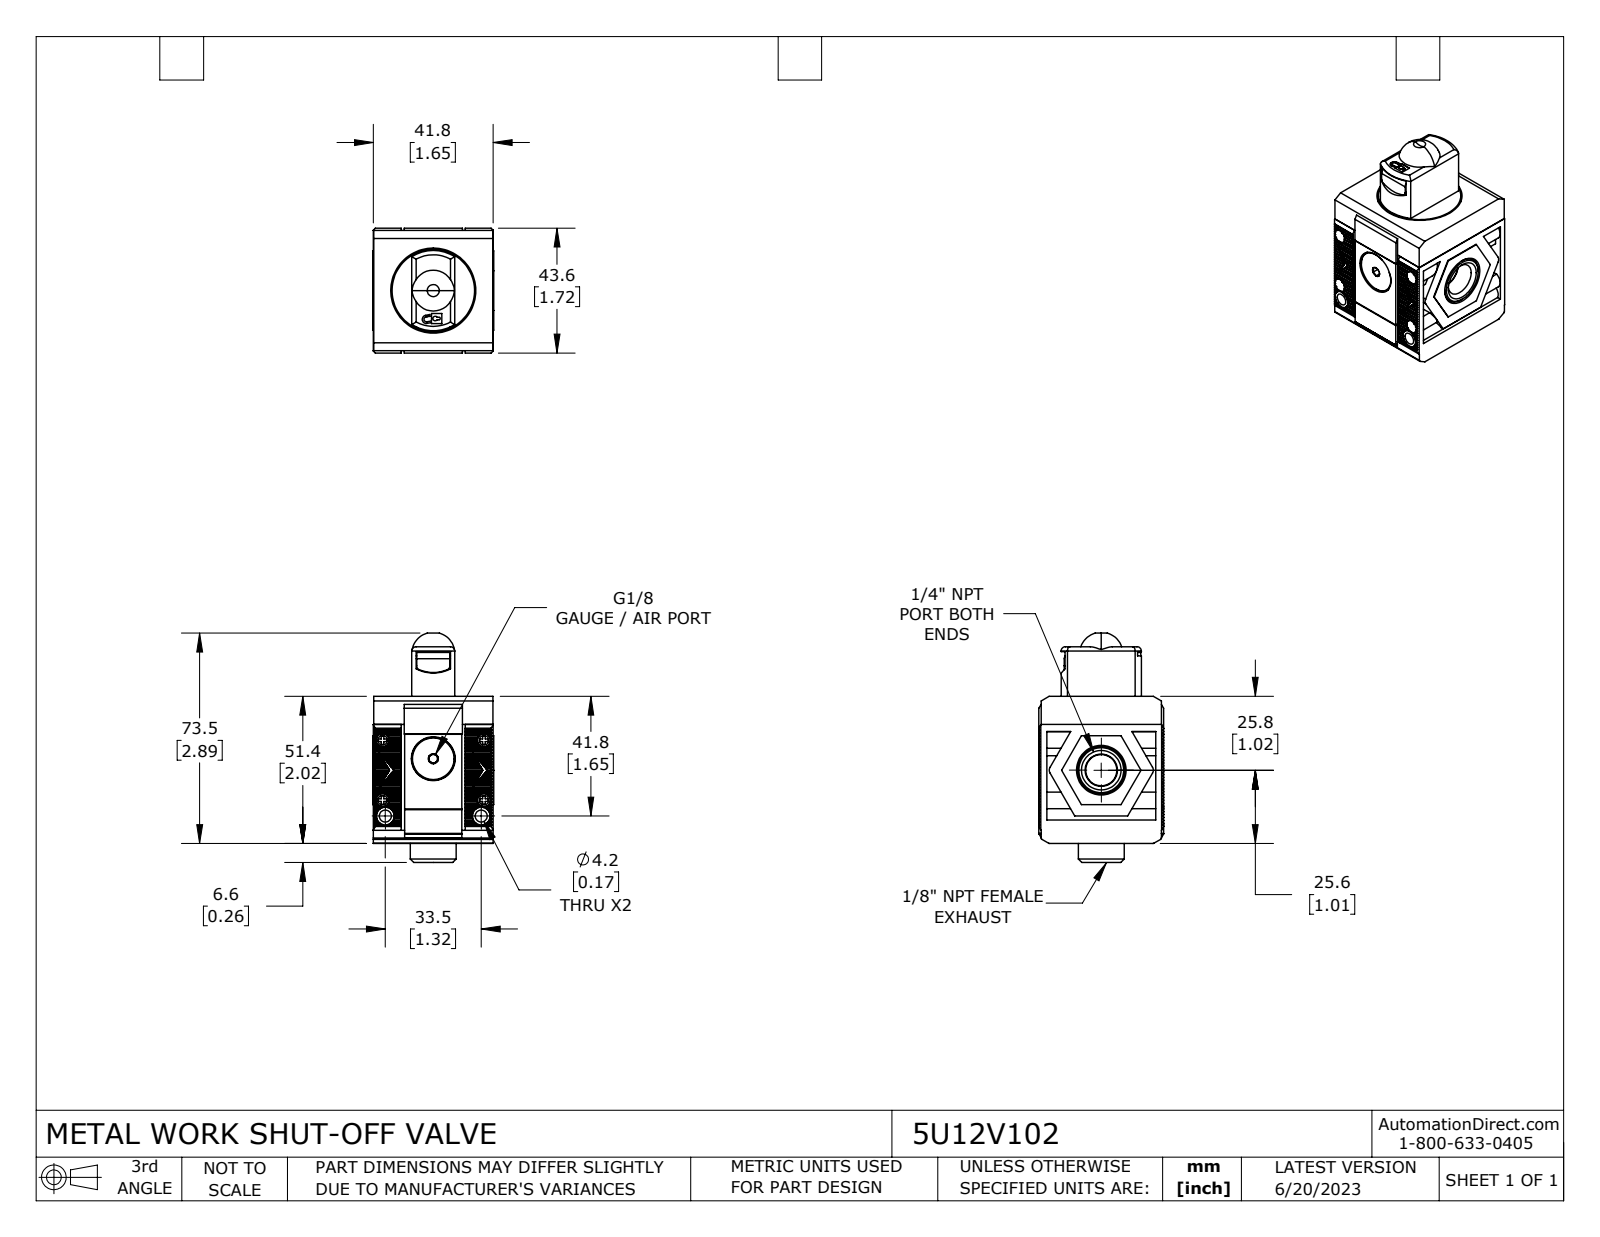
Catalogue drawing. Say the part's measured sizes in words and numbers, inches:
The part is named "5U12V102". Its 3-D file was written by "SolidWorks 2021 (CONFIG_CONTROL_DESIGN)". It is 13 solids with 1159 faces: 817 planar, 206 cylindrical and 136 other. Overall it measures 3.152 by 1.717 by 1.661 inches. Its volume is 5.793 cubic inches and its surface area 53.4 square inches. Round holes: 4 of diameter 0.083, 4 of diameter 0.118, 4 of diameter 0.185, 2 of diameter 0.165, 2 of diameter 0.337, 1 of diameter 0.602, 1 of diameter 1.169, 1 of diameter 1.232. Round bosses or shafts: 4 of diameter 0.181, 4 of diameter 0.102, 2 of diameter 0.244, 1 of diameter 1.26, 1 of diameter 1.134, 1 of diameter 0.898, 1 of diameter 0.717, 1 of diameter 0.63. Partial cylindrical surfaces (rounded edges, fillets, slot ends): 4 of radius 0.024, 4 of radius 0.059, 4 of radius 0.122, 2 of radius 0.008, 2 of radius 0.079, 1 of radius 0.018, 1 of radius 0.033, 1 of radius 0.039. The main face-to-face distances are 1.638, 1.339, 1.642, 0.307, 1.673, 0.386, 2.024, 0.043, 1.654, 0.031. The hole center spacings are 0.222, 0.742, 0.823, 0.9, 1.027, 1.042, 1.374, 1.394.
